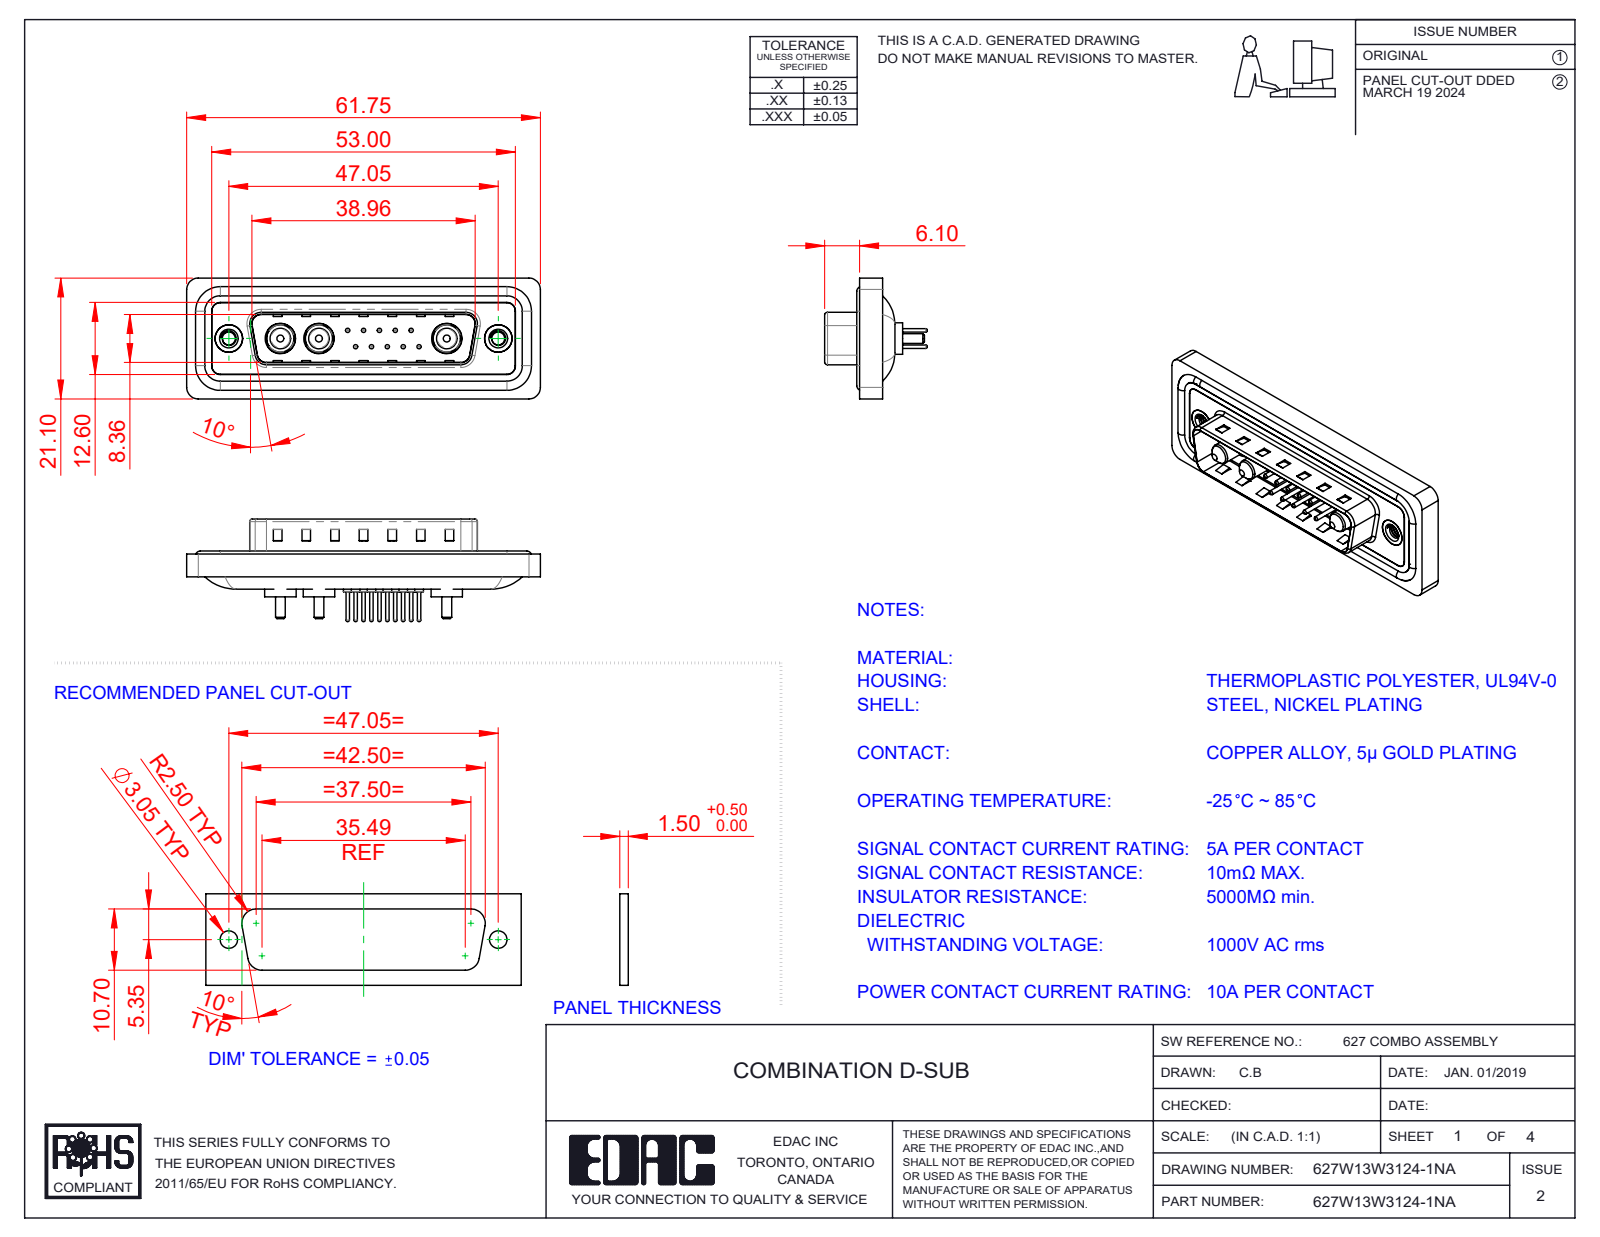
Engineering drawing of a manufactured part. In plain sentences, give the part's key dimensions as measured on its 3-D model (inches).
The part is named "627Combo Waterproof Housing_25 Contacts; 627W13W3124-1NA; 627Combo Contact Row 1_24; 627Combo Shell Front_25 Contacts (+5 more)". Its 3-D file was written by "SolidWorks 2023 (CONFIG_CONTROL_DESIGN)". It is 23 solids with 968 faces: 309 planar, 387 cylindrical and 272 other. Overall it measures 2.431 by 0.831 by 0.705 inches. Its volume is 0.445 cubic inches and its surface area 18.34 square inches. Round holes: 10 of diameter 0.03, 10 of diameter 0.063, 10 of diameter 0.079, 3 of diameter 0.191, 3 of diameter 0.209, 2 of diameter 0.089, 2 of diameter 0.157, 2 of diameter 0.189, 2 of diameter 0.197. Round bosses or shafts: 10 of diameter 0.059, 10 of diameter 0.024, 4 of diameter 0.063, 3 of diameter 0.217, 3 of diameter 0.205, 3 of diameter 0.187, 3 of diameter 0.148, 3 of diameter 0.142. Partial cylindrical surfaces (rounded edges, fillets, slot ends): 22 of radius 0.059, 18 of radius 0.079, 8 of radius 0.02, 8 of radius 0.063, 4 of radius 0.01, 4 of radius 0.024, 4 of radius 0.026, 4 of radius 0.035. The main face-to-face distances are 0.016, 0.059, 0.043, 0.063, 0.02, 0.122, 0.114, 0.032, 0.377, 0.161. The hole center spacings are 0.124, 0.109, 0.198, 0.218, 0.295, 0.198, 0.327, 0.398.
